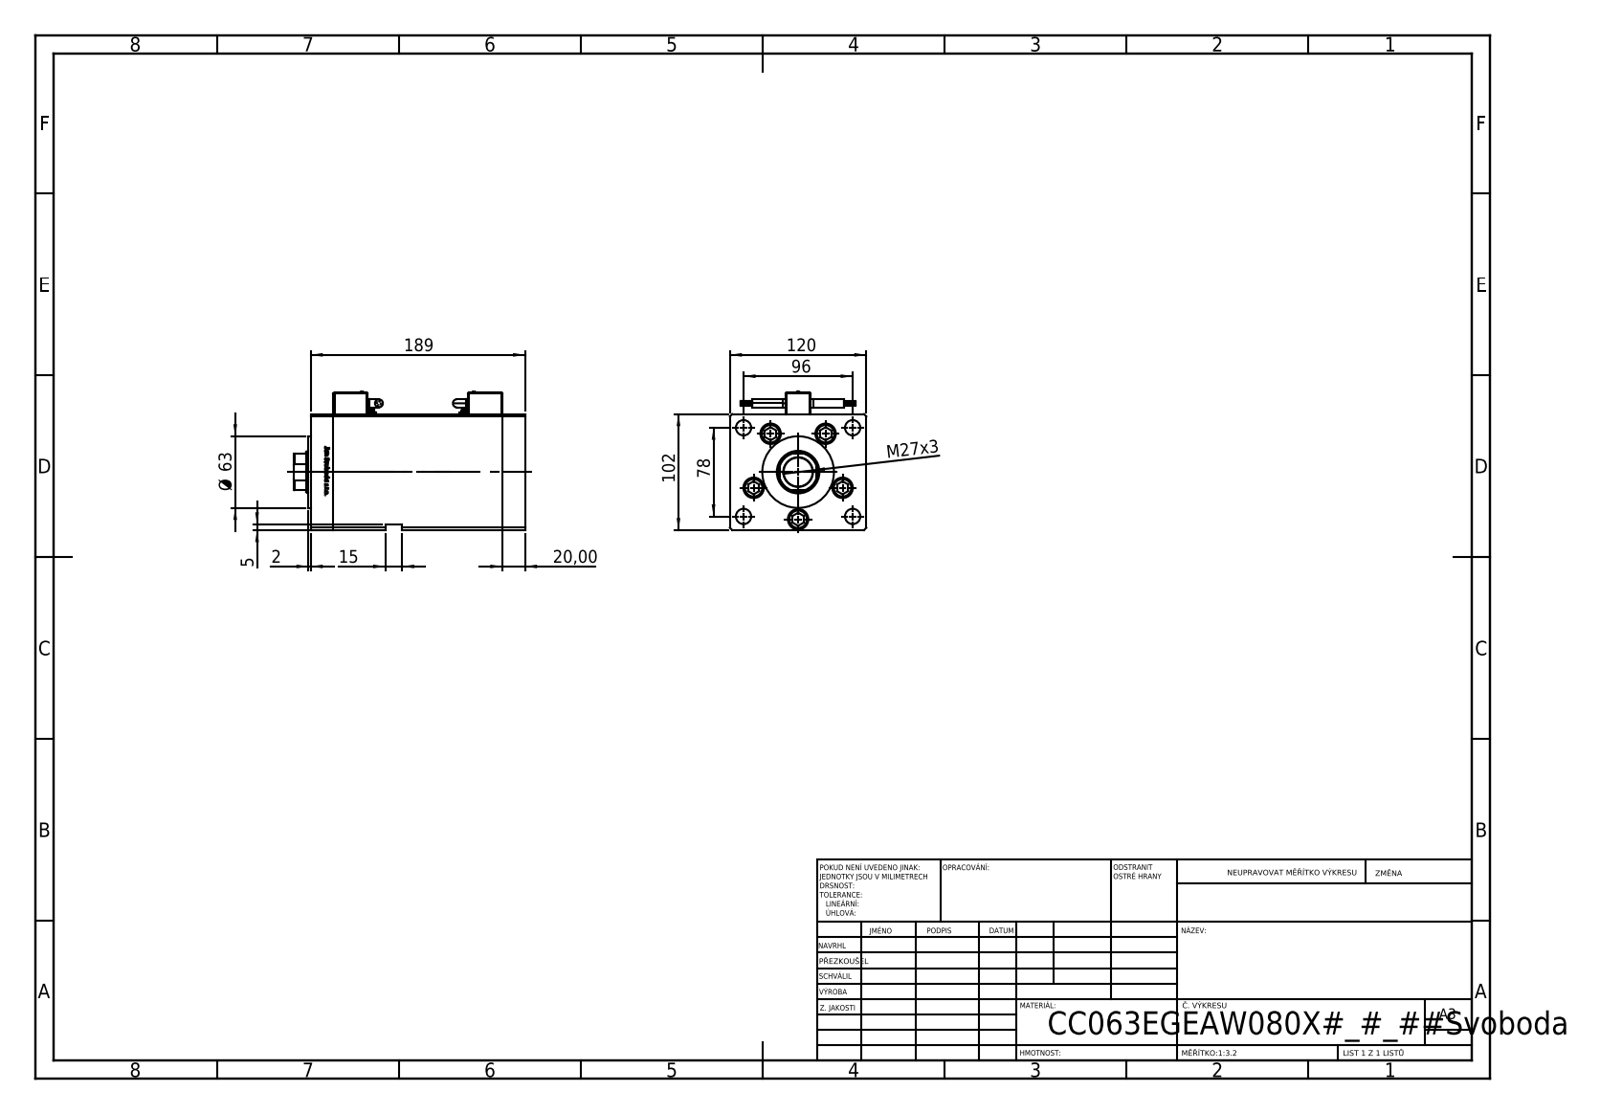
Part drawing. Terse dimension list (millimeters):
name: Magnetic_Switch_MSU4; V220C_E MIDDLE; ALLEN BOLT; V220C_VC_E (+2 more)
written by: SolidWorks 2019 (CONFIG_CONTROL_DESIGN)
unit: mm
bodies: 16 solids, 1419 faces (553 planar, 256 cylindrical, 610 other)
size: 203.5 × 122.1 × 120
volume: 2 010 000 mm³; area: 285 109 mm²
holes: 9× ⌀13.5, 5× ⌀18, 4× ⌀12.5, 4× ⌀18.5, 2× ⌀2, 2× ⌀3.6, 2× ⌀5, 2× ⌀7, 1× ⌀13.16, 1× ⌀25.5, 1× ⌀36, 1× ⌀37.5
bosses: 8× ⌀0.85, 5× ⌀17, 5× ⌀8, 4× ⌀7, 2× ⌀6, 2× ⌀3.5, 2× ⌀2.5, 1× ⌀63
rounds: 24× R1, 4× R4, 2× R0.93, 1× R6.58, 1× R17.5
face distances: 120, 20, 148.5, 168.5, 102, 34.25, 188.5, 14.25, 134.25, 154.25
hole spacings: 41.5, 61.85, 8.25, 24.39, 26.69, 45.54, 47.51, 47.92
